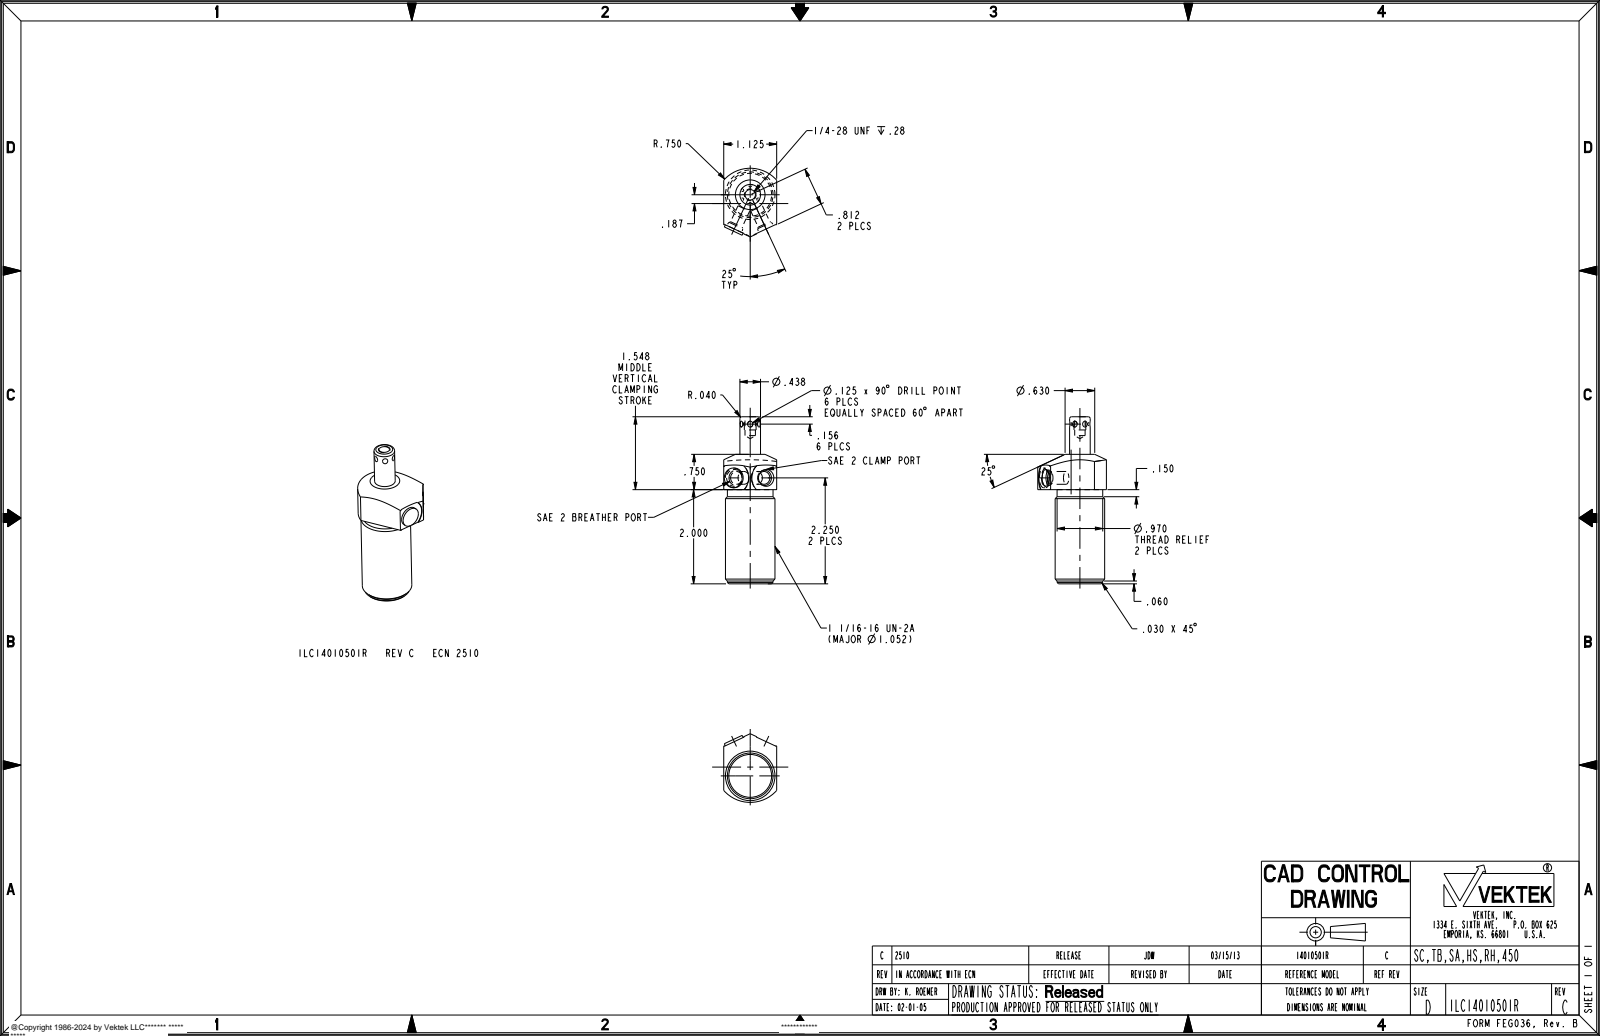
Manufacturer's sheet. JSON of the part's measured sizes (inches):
{"part_name": "ILC14010501R", "step_written_by": "PRO/ENGINEER BY PARAMETRIC TECHNOLOGY CORPORATION, 2007460 (AUTOMOTIVE_DESIGN_CC2)", "units": "inches", "bodies": {"solids": 1, "faces": 76, "planar": 19, "cylindrical": 25, "other": 32}, "overall_size": [3.548, 1.459, 1.125], "volume_in3": 2.687, "surface_area_in2": 14.74, "round_holes": [[0.272, 2], [0.221, 1]], "round_bosses_or_shafts": [[1.052, 1], [0.97, 1], [0.438, 1], [0.418, 1], [0.25, 1]], "partial_cylinders_radius": [[0.341, 2], [0.75, 1]], "face_to_face_distances": [2, 1.125, 2.75, 0.75, 0.05, 0.48, 0.05, 3.548, 1.548, 0.798]}
